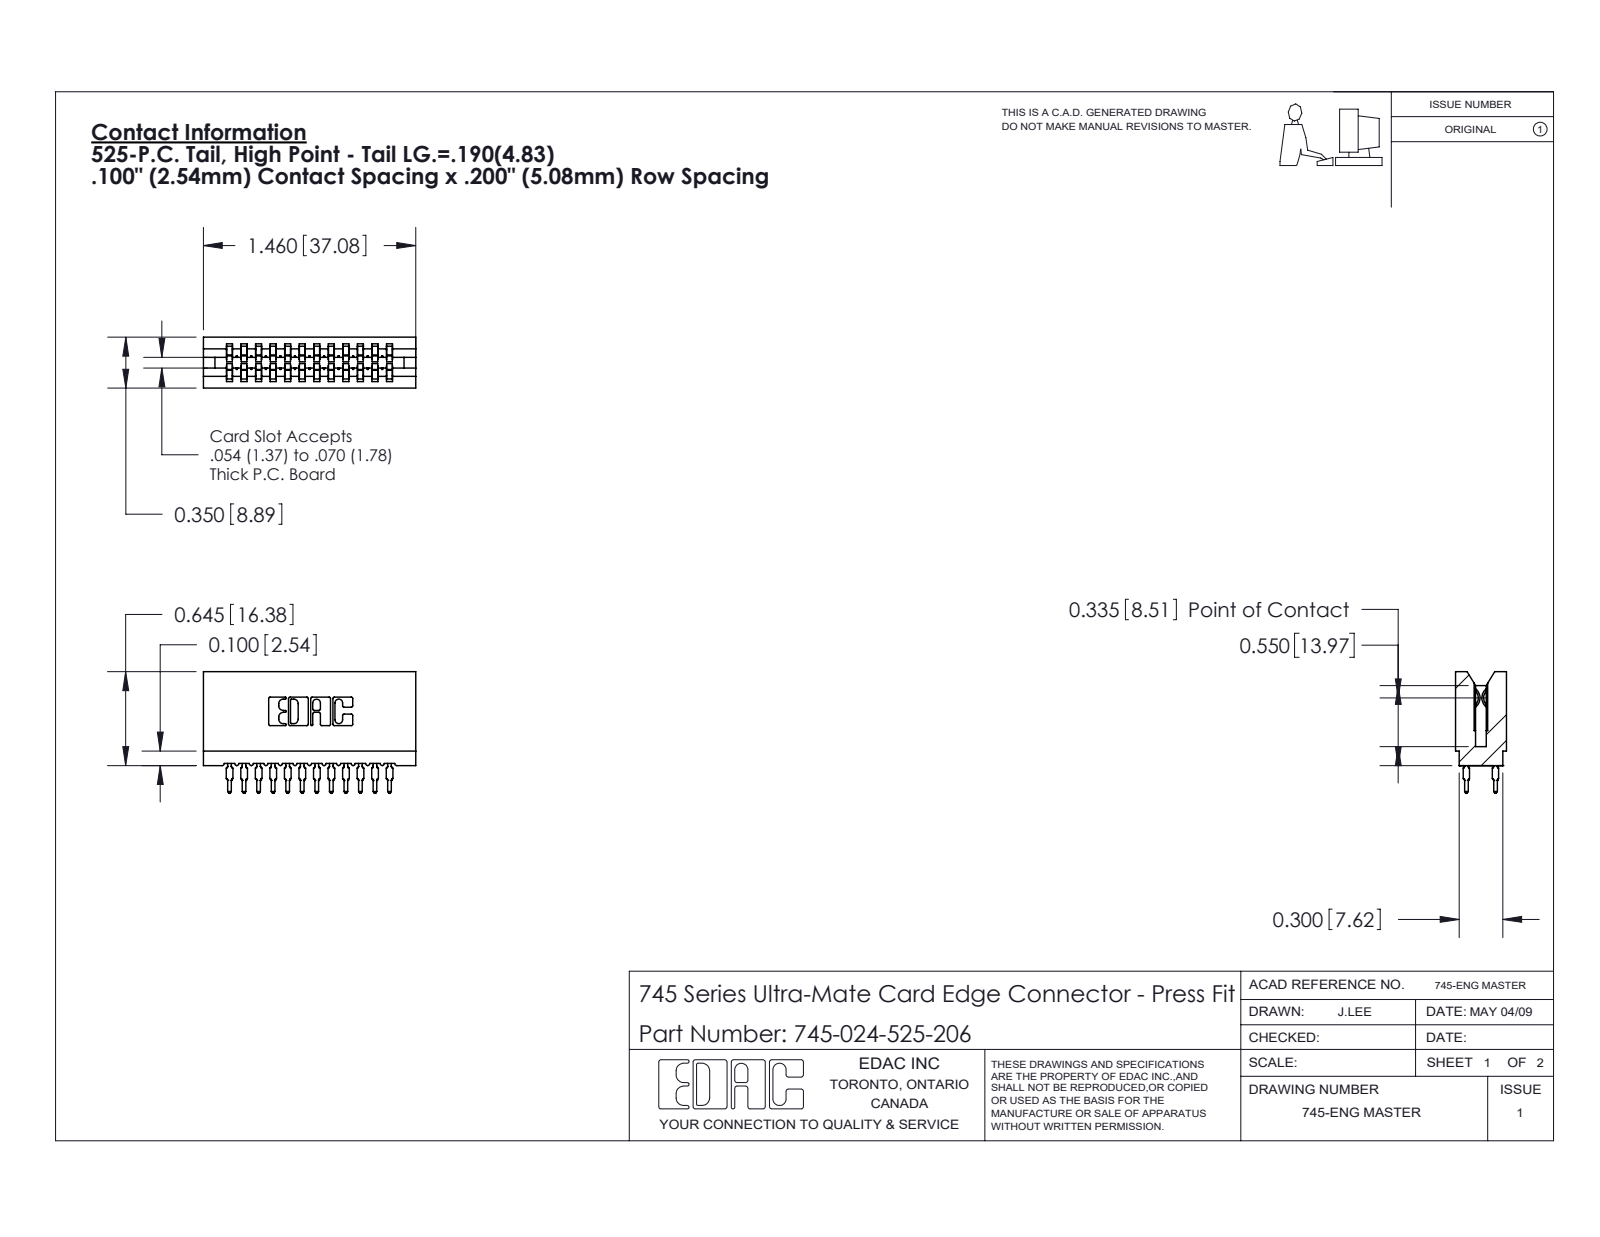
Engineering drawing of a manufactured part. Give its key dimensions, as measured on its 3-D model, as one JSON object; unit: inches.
{"part_name": "745-024-525-206; 745-292-001_525; 745 Part_Insulator Option - 06", "step_written_by": "SolidWorks 2020 (CONFIG_CONTROL_DESIGN)", "units": "inches", "bodies": {"solids": 25, "faces": 2244, "planar": 1160, "cylindrical": 460, "other": 624}, "overall_size": [1.46, 0.836, 0.35], "volume_in3": 0.213, "surface_area_in2": 9.935, "partial_cylinders_radius": [[0.021, 48], [0.015, 24], [0.01, 22], [0.005, 8], [0.011, 8], [0.007, 6], [0.031, 6], [0.026, 3]], "face_to_face_distances": [0.2, 0.1, 0.3, 0.4, 0.5, 0.058, 0.6, 0.042, 0.35, 0.358]}
